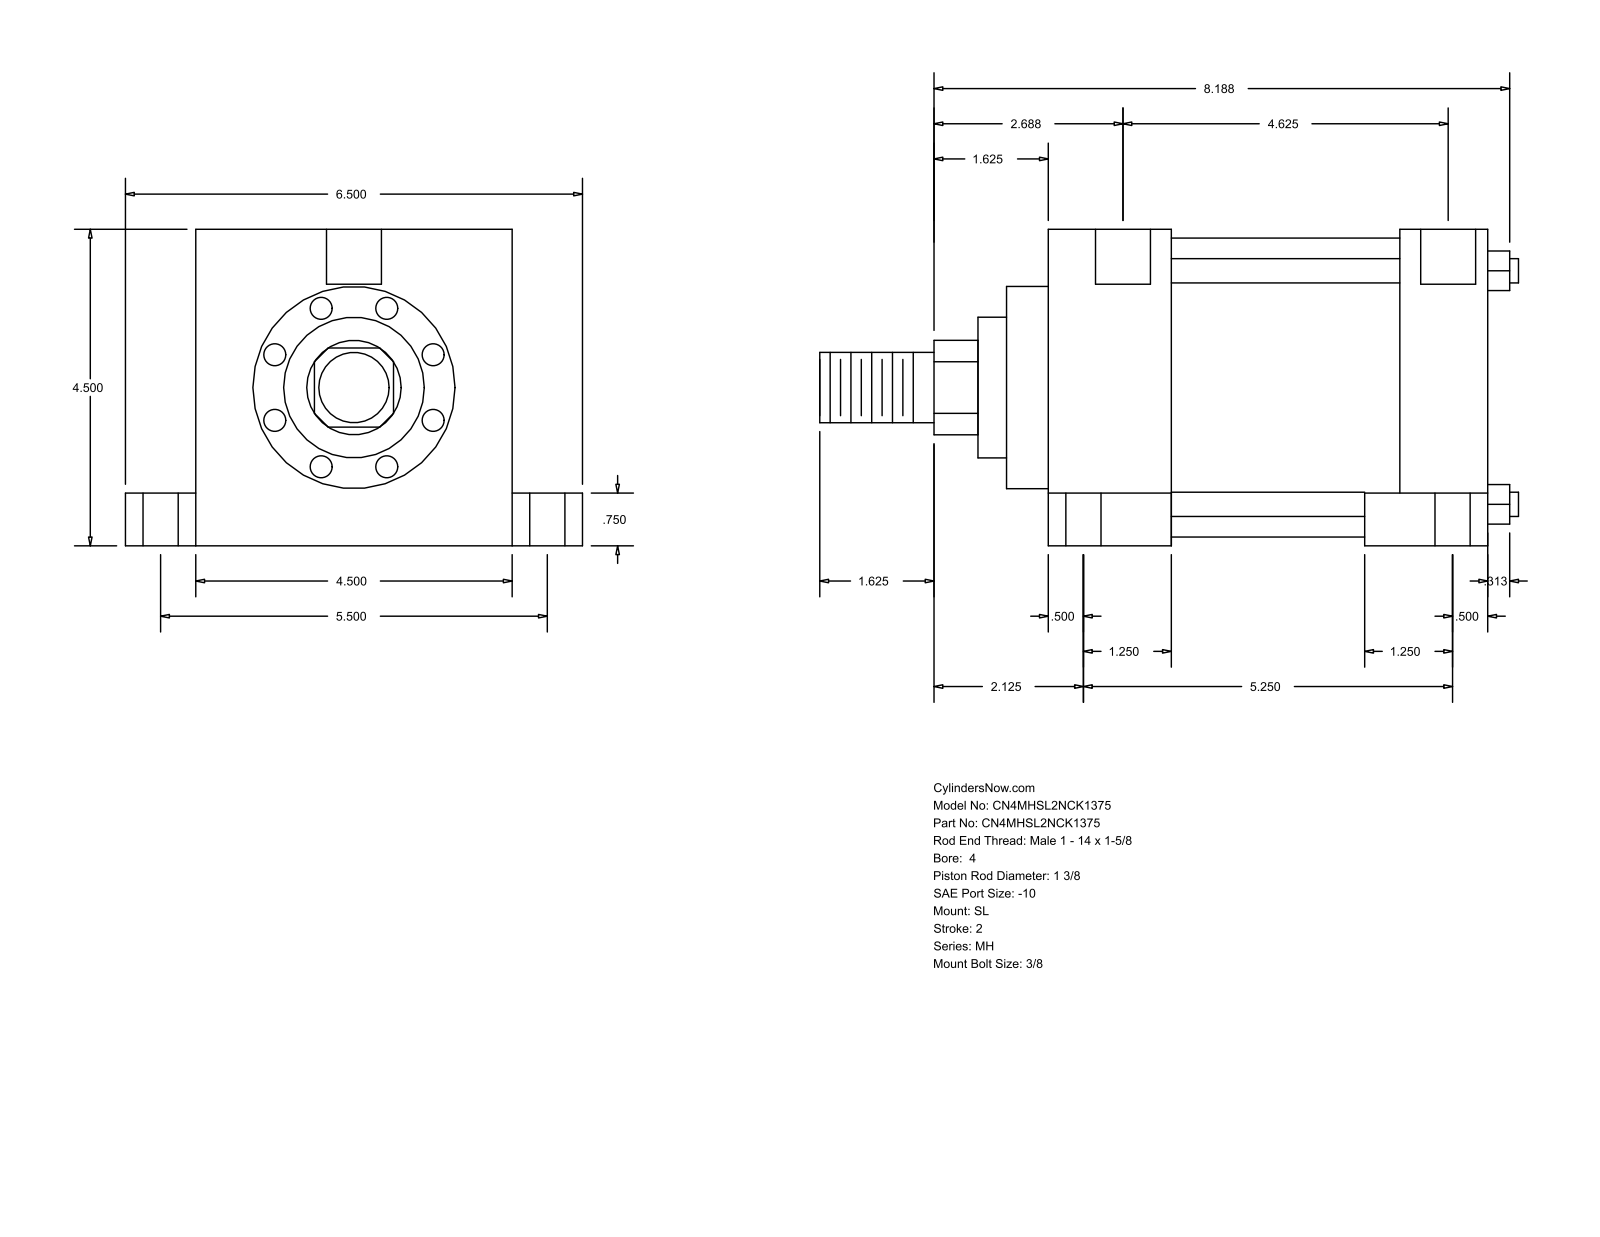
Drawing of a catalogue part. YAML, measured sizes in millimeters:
part_name: "MH_SL__0400_1.375"
step_written_by: "GSSL Pune (CONFIG_CONTROL_DESIGN)"
units: millimeters
bodies: {solids: 0, faces: 110, planar: 77, cylindrical: 33, other: 0}
overall_size: [252.41, 165.1, 114.3]
round_holes:
  - {diameter: 8.73, count: 4}
  - {diameter: 12.7, count: 4}
  - {diameter: 19.05, count: 4}
  - {diameter: 19.84, count: 2}
round_bosses_or_shafts:
  - {diameter: 8.76, count: 4}
  - {diameter: 107.95, count: 1}
  - {diameter: 73.03, count: 1}
  - {diameter: 50.8, count: 1}
  - {diameter: 34.92, count: 1}
  - {diameter: 25.4, count: 1}
partial_cylinders:
  - {radius: 17.06, count: 1}
face_to_face_distances: [114.3, 158.76, 44.45, 114.31, 127.01, 82.56, 31.75, 25.4, 139.7, 19.05]
hole_center_spacings: [69.85, 69.87, 70.99, 71.29, 120.65, 133.34, 138.04, 139.41]
